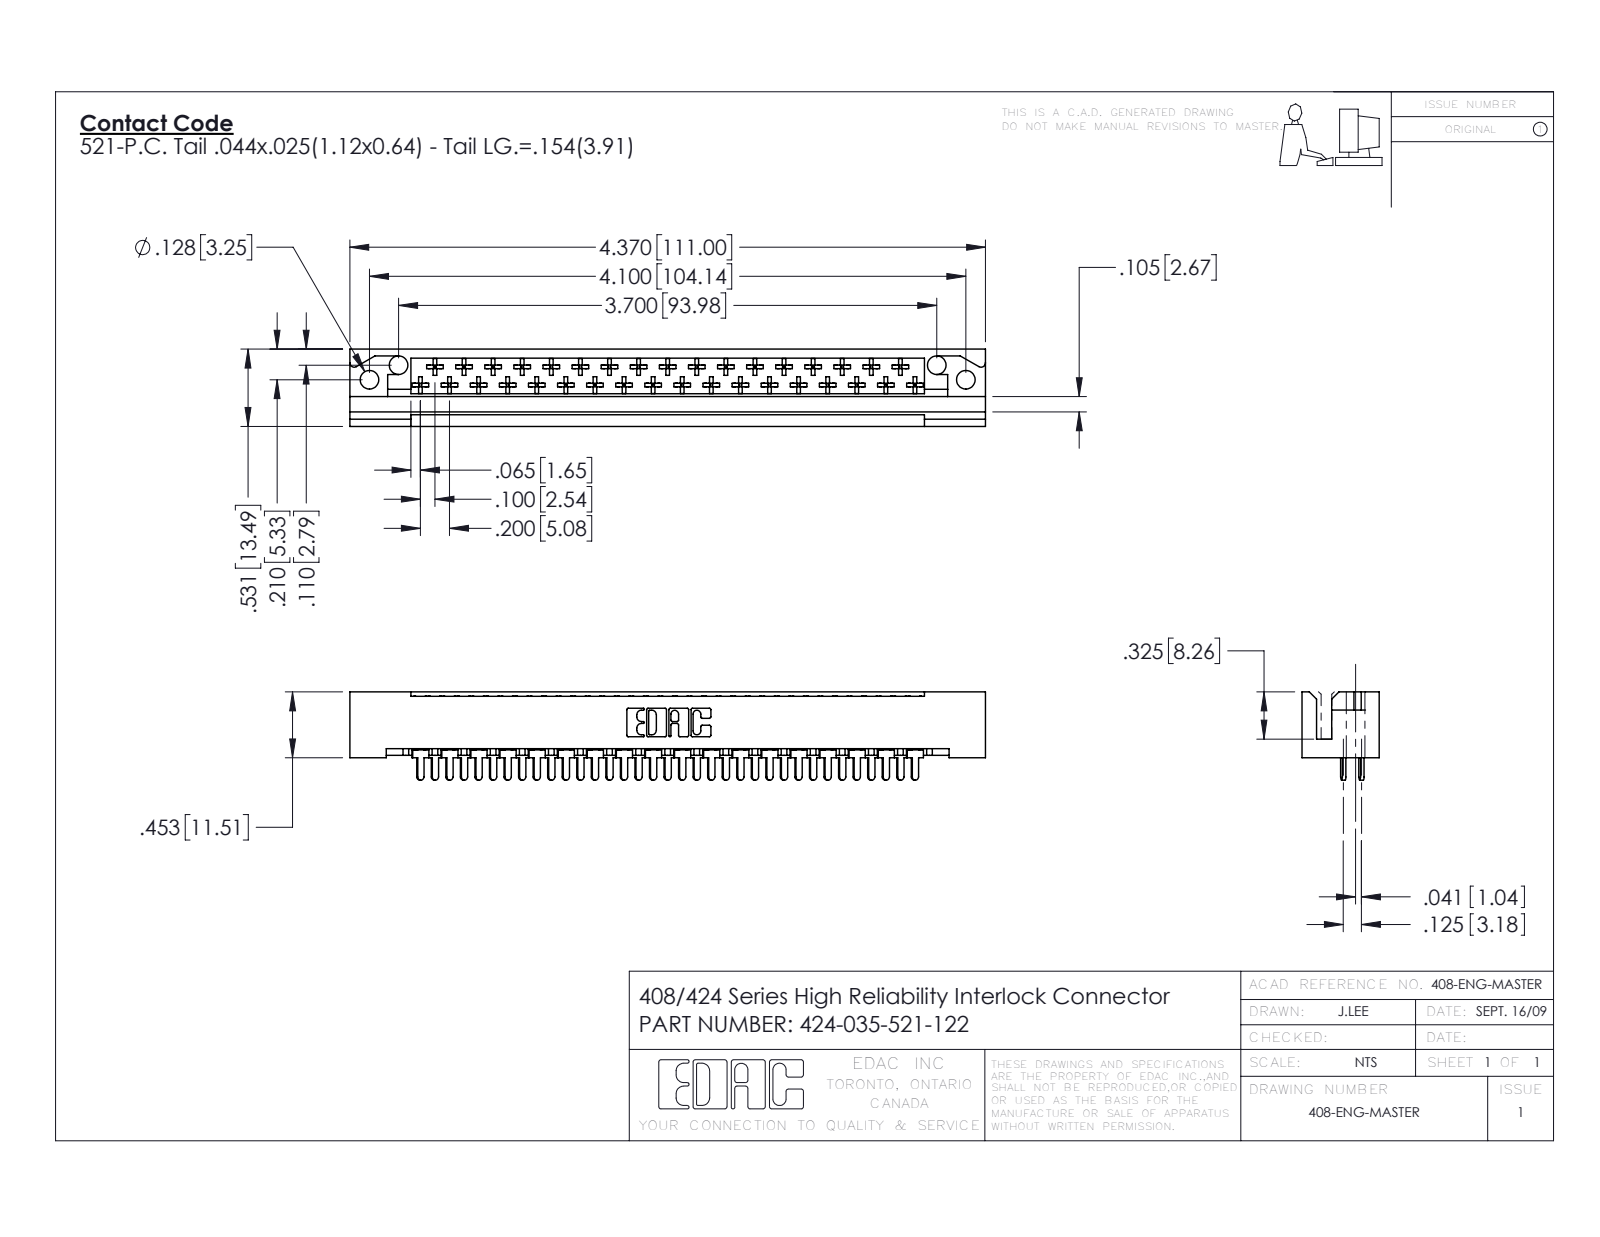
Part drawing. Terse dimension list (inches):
name: 408-290-001_408-290-121; 424-035-521-122; 424 Part_035
written by: SolidWorks 2016 (CONFIG_CONTROL_DESIGN)
unit: in
bodies: 36 solids, 2070 faces (1559 planar, 371 cylindrical, 140 other)
size: 4.37 × 0.607 × 0.531
volume: 0.7 in³; area: 23.23 in²
holes: 4× ⌀0.128
rounds: 210× R0.01, 37× R0.02, 35× R0.022, 22× R0.01, 6× R0.007, 6× R0.031, 3× R0.026, 2× R0.03
face distances: 0.1, 0.296, 0.025, 0.531, 0.125, 0.217, 0.272, 0.235, 0.259, 0.025
hole spacings: 0.224, 3.901, 3.7, 4.1
